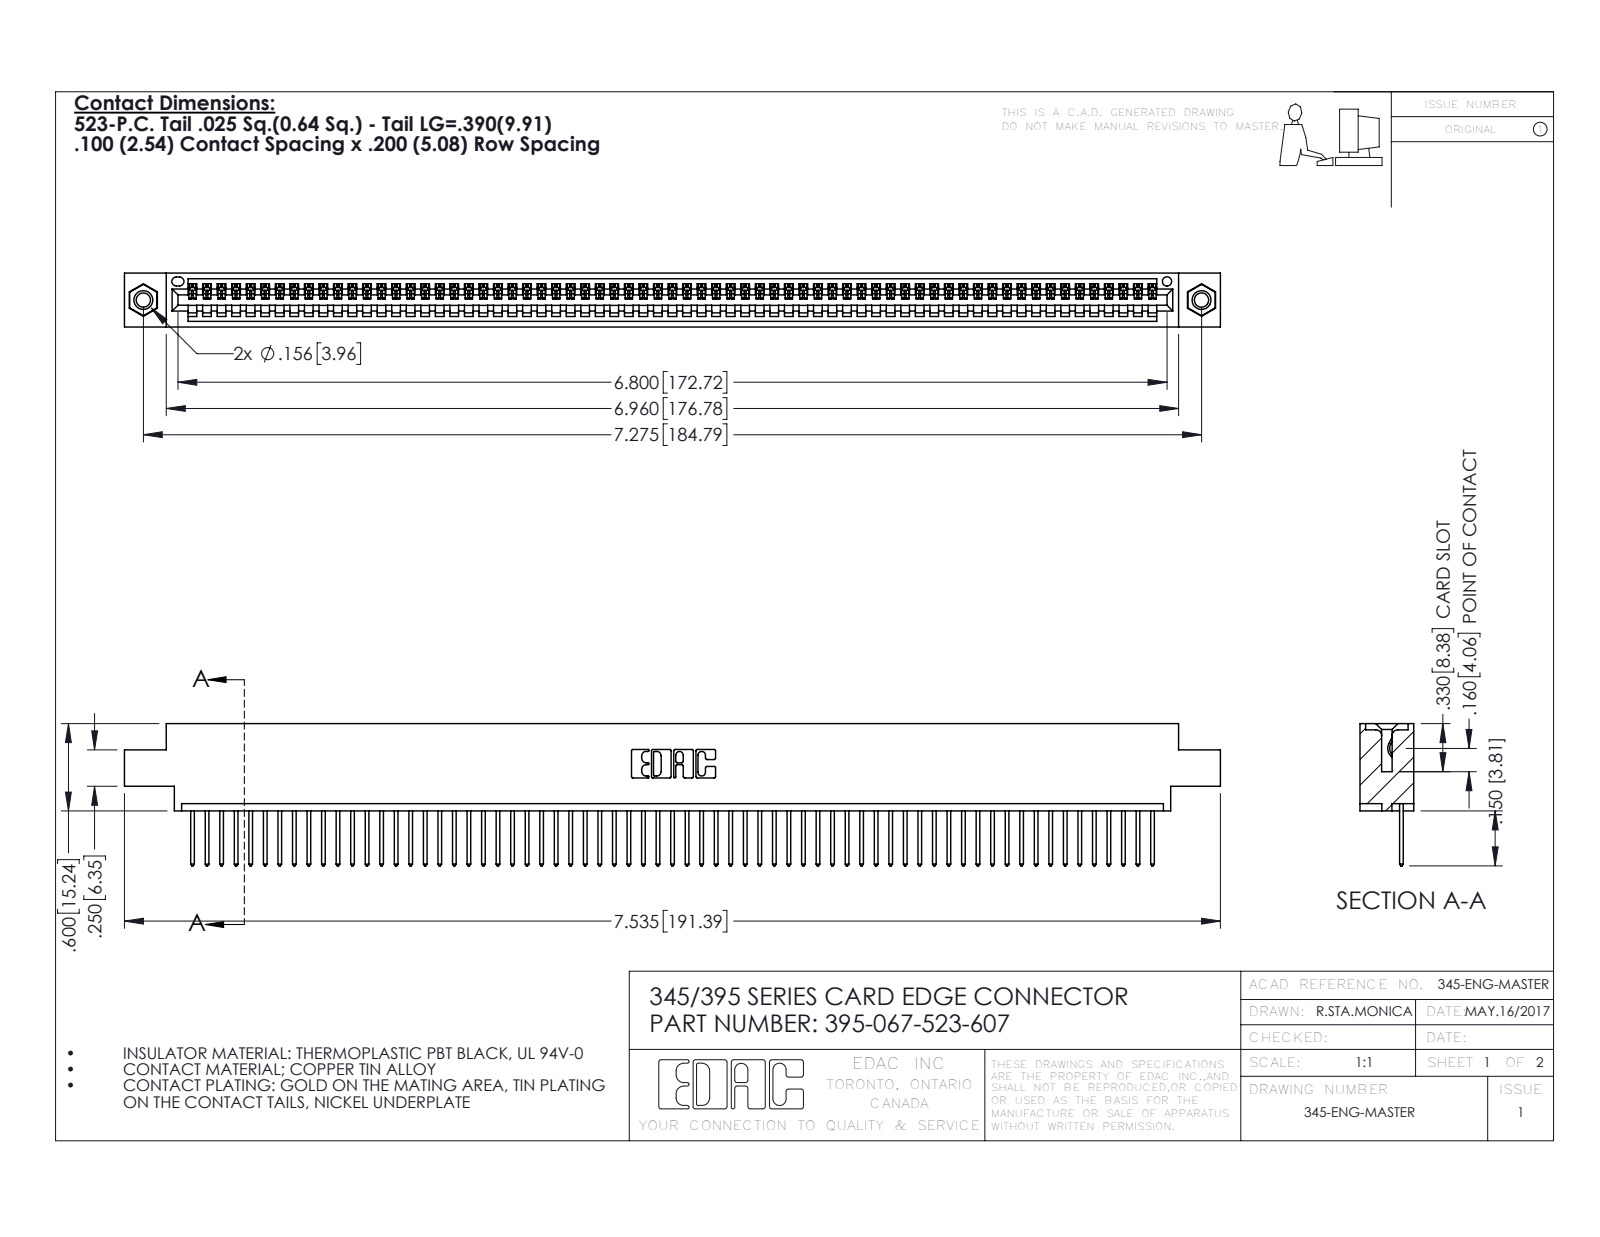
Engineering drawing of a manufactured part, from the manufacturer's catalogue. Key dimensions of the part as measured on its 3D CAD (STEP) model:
Part name (STEP PRODUCT): 345-250-001_345-250-005-103; 395-067-523-607; 345-292-001_345-293-123; 345 Part_0.170 Offset - 0.156 Dia-TI
STEP written by: SolidWorks 2016 (CONFIG_CONTROL_DESIGN)
Units: inches
Bodies: 70 solids, 4076 faces (2796 planar, 1264 cylindrical, 16 other)
Overall size (bounding box): 7.535 × 0.977 × 0.37
Volume: 1.112 in³ · Surface area: 38.44 in²
Round holes (diameter × count): ⌀0.098 ×2, ⌀0.125 ×2, ⌀0.156 ×2, ⌀0.064 ×1
Round bosses / shafts (diameter × count): ⌀0.155 ×2
Partial cylindrical surfaces — rounded edges, fillets, slot ends (radius × count): R0.006 ×134, R0.01 ×134, R0.01 ×22, R0.007 ×6, R0.031 ×6, R0.026 ×3, R0.031 ×2, R0.04 ×2
Main face-to-face distances: 0.072, 0.298, 0.37, 0.098, 0.272, 0.025, 0.2, 0.225, 0.175, 0.149
Hole centre spacings: 0.27, 7.039, 7.275
